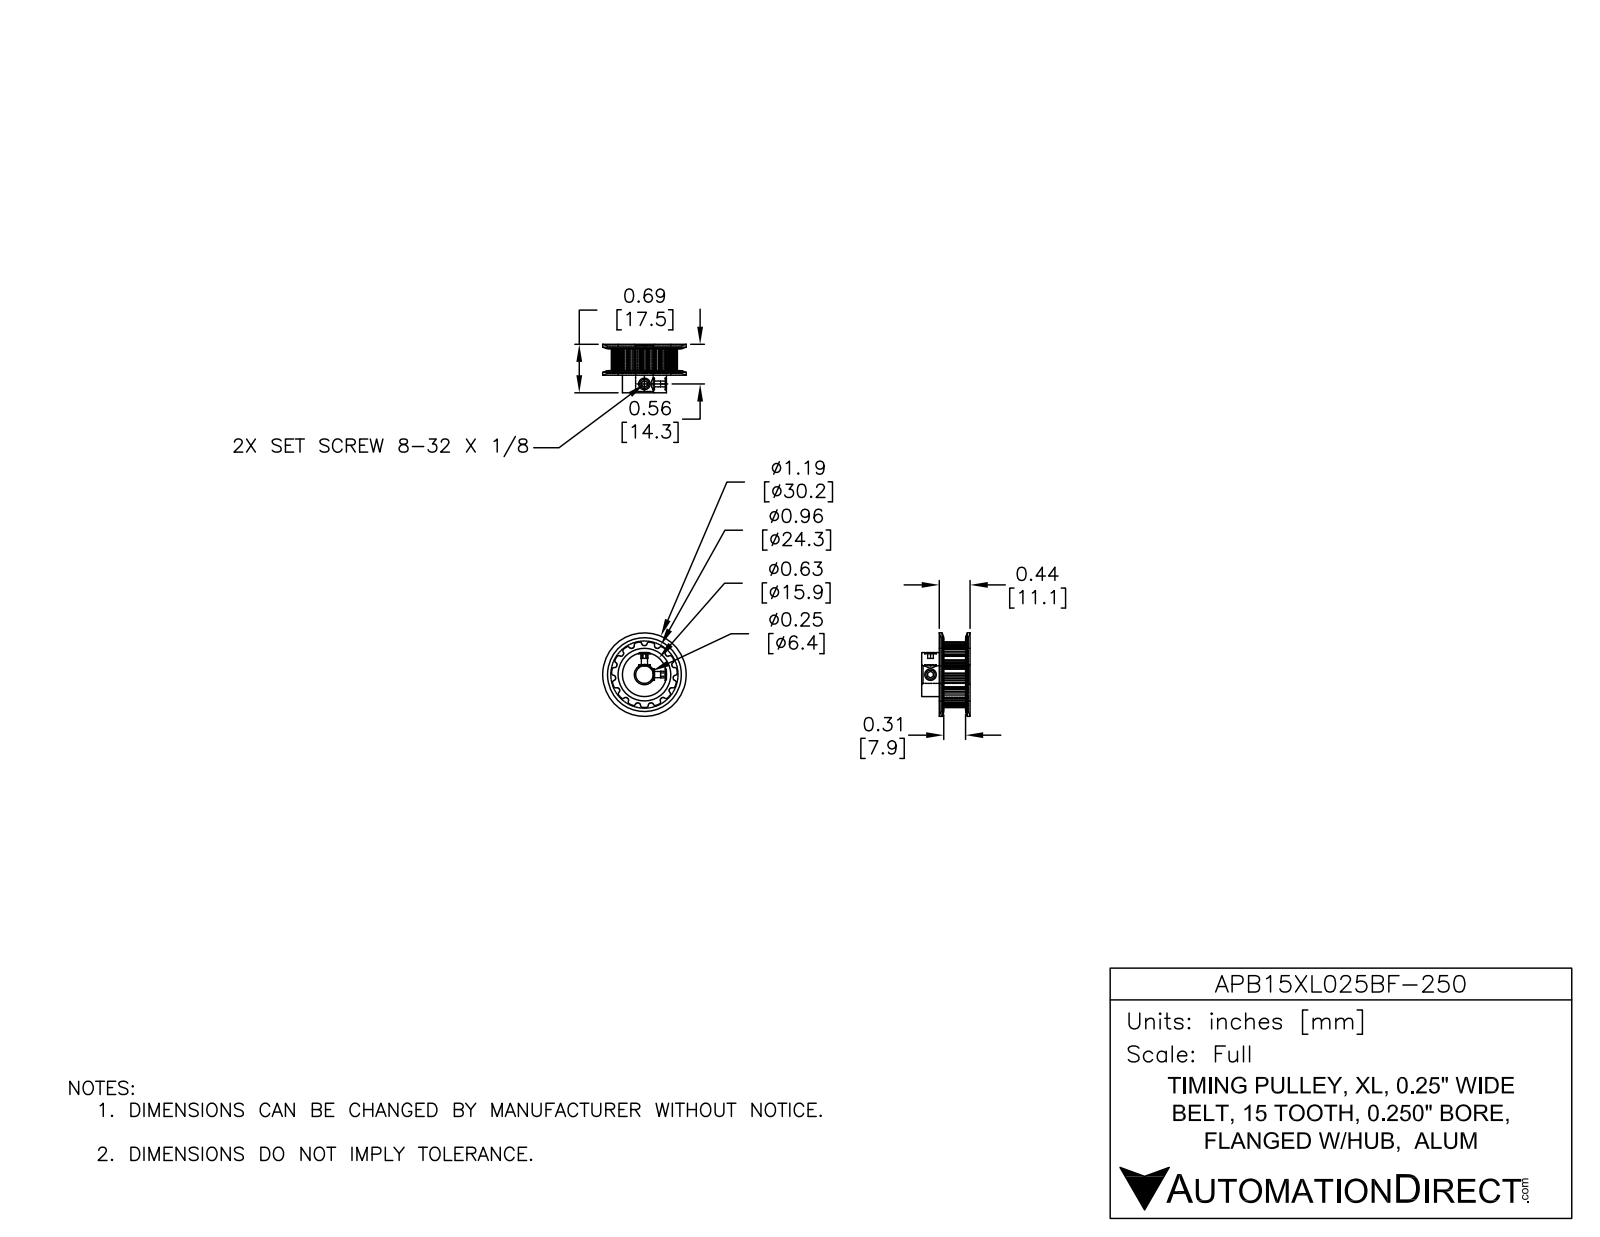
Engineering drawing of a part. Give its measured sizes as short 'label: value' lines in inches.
name: APB15XL025BF-250
written by: SolidWorks 2014 (AUTOMOTIVE_DESIGN)
unit: in
bodies: 1 solid, 170 faces (51 planar, 97 cylindrical, 22 other)
size: 1.188 × 1.188 × 0.688
volume: 0.325 in³; area: 5.7 in²
holes: 2× ⌀0.088, 1× ⌀0.25
bosses: 1× ⌀0.625
rounds: 60× R0.015, 1× R0.413
face distances: 0.375, 0.033, 0.407, 0.688, 0.656, 0.281, 0.032, 0.343, 0.375, 0.313
